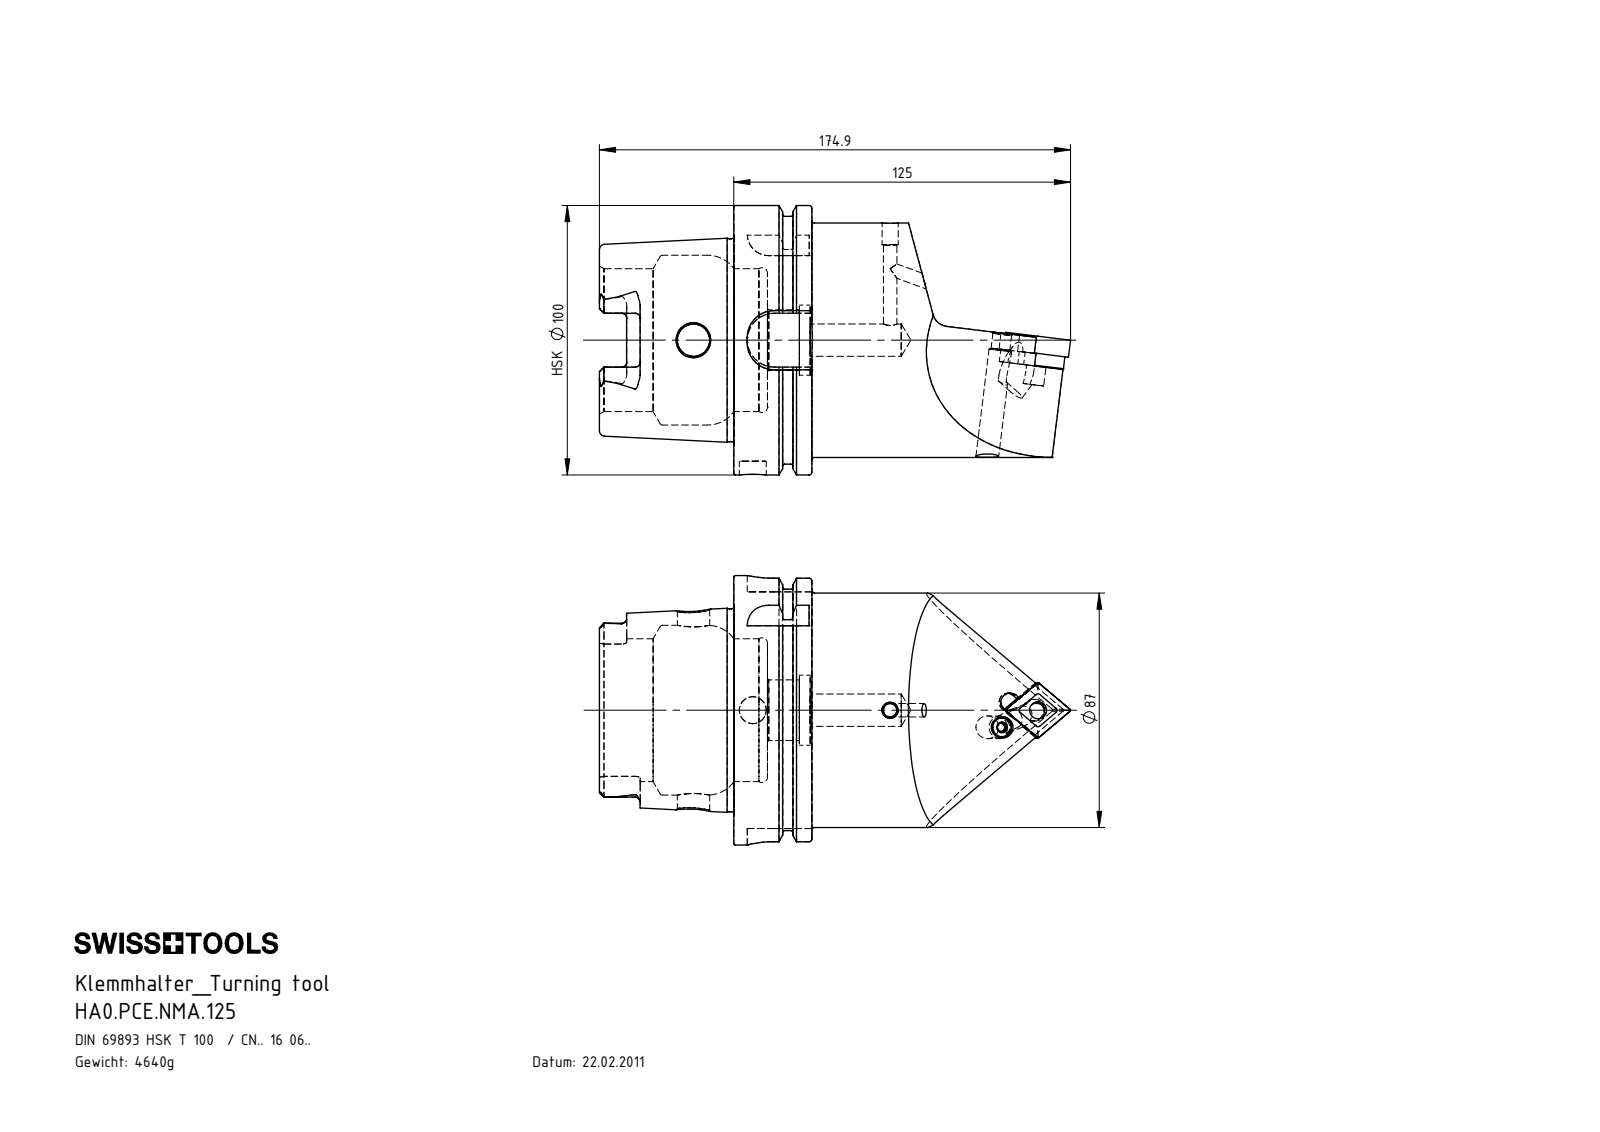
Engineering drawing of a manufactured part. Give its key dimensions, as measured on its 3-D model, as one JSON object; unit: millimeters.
{"part_name": "HA0-PCE.NMA.125; WCE-ER4.101.020_A; CNMG160604; WCE-ER2.101.004_A (+3 more)", "step_written_by": "SolidWorks 2012 (CONFIG_CONTROL_DESIGN)", "units": "millimeters", "bodies": {"solids": 7, "faces": 360, "planar": 113, "cylindrical": 99, "other": 148}, "overall_size": [174.9, 100, 100], "volume_mm3": 589895, "surface_area_mm2": 73342, "round_holes": [[5, 2], [12, 2], [6.35, 1], [7, 1], [8.05, 1], [8.4, 1], [10, 1], [22.5, 1], [26, 1], [53, 1], [63, 1]], "round_bosses_or_shafts": [[6, 2], [100, 1], [91.95, 1], [87, 1], [75.26, 1], [8, 1], [7.9, 1], [6.4, 1]], "partial_cylinders_radius": [[1.9, 6], [0.4, 4], [1.5, 4], [3.5, 3], [10, 3], [4.83, 2], [4.88, 2], [3.1, 1]], "face_to_face_distances": [12.45, 28.95, 16.5, 49.9, 62.35, 78.85, 87.8, 78.2, 28.3, 15.85], "hole_center_spacings": [14.75, 15, 51]}
